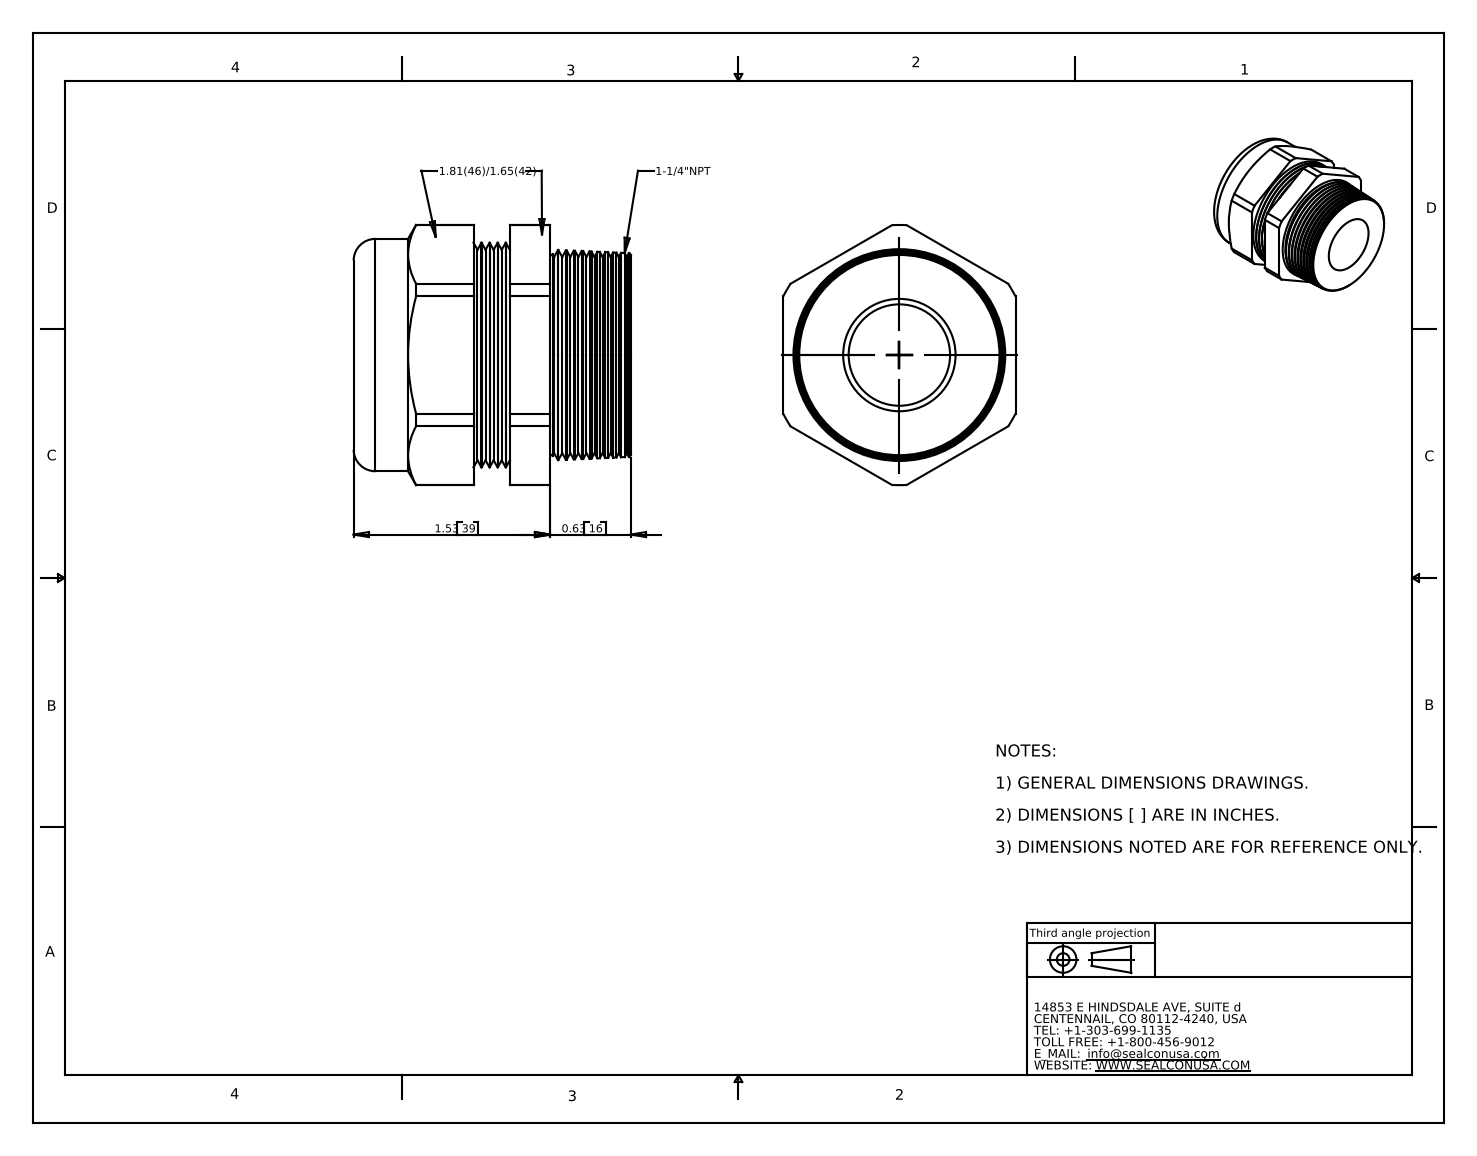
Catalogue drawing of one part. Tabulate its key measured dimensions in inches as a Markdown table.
| quantity | value |
| --- | --- |
| part name | CD29LR-BK |
| STEP written by | SolidWorks 2007 (CONFIG_CONTROL_DESIGN) |
| units | inches |
| bodies | 2 solids, 150 faces (20 planar, 32 cylindrical, 98 other) |
| overall size | 2.16 × 2.027 × 1.81 |
| volume | 4.094 in³ |
| surface area | 32.59 in² |
| round holes (diameter × count) | 0.79 × 1, 1.394 × 1 |
| round bosses / shafts (diameter × count) | 1.81 × 1, 1.749 × 1 |
| partial cylindrical surfaces (radius × count) | 1.014 × 1 |
| main face-to-face distances | 1.81, 1.736, 0.404, 2.14, 1.51, 1.106, 0.63, 1.196, 0.793, 0.313 |
